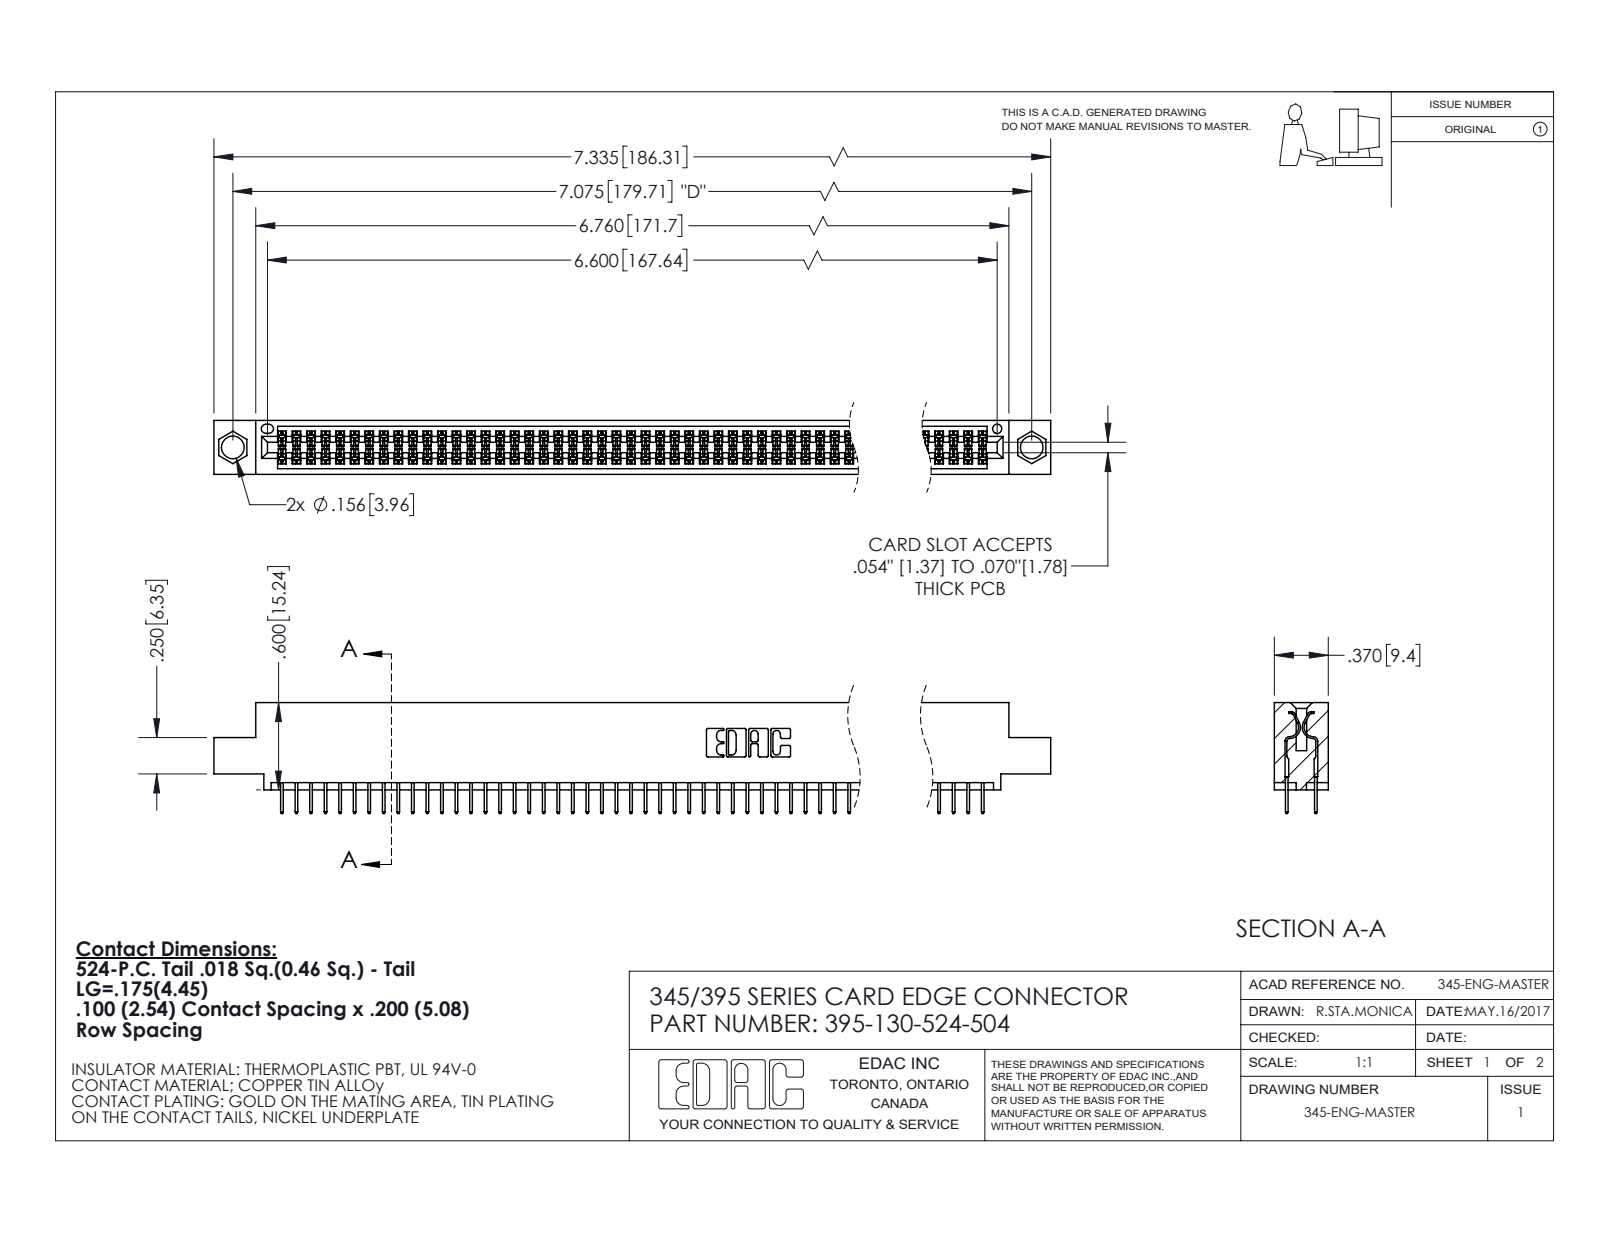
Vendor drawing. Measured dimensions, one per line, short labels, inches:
name: 345-292-001_345-293-124; 395-130-524-504; 345 Part_0.110 Offset - 0.156 Dia-TI
written by: SolidWorks 2020 (CONFIG_CONTROL_DESIGN)
unit: in
bodies: 131 solids, 7164 faces (5168 planar, 1996 cylindrical, 0 other)
size: 7.335 × 0.762 × 0.37
volume: 1.095 in³; area: 40.89 in²
holes: 2× ⌀0.156, 1× ⌀0.064
rounds: 195× R0.006, 22× R0.01, 6× R0.007, 6× R0.031, 3× R0.026, 2× R0.014, 2× R0.019, 2× R0.022
face distances: 0.072, 0.298, 0.2, 0.37, 0.098, 0.272, 0.025, 0.225, 0.072, 0.175
hole spacings: 0.27, 6.839, 7.075
